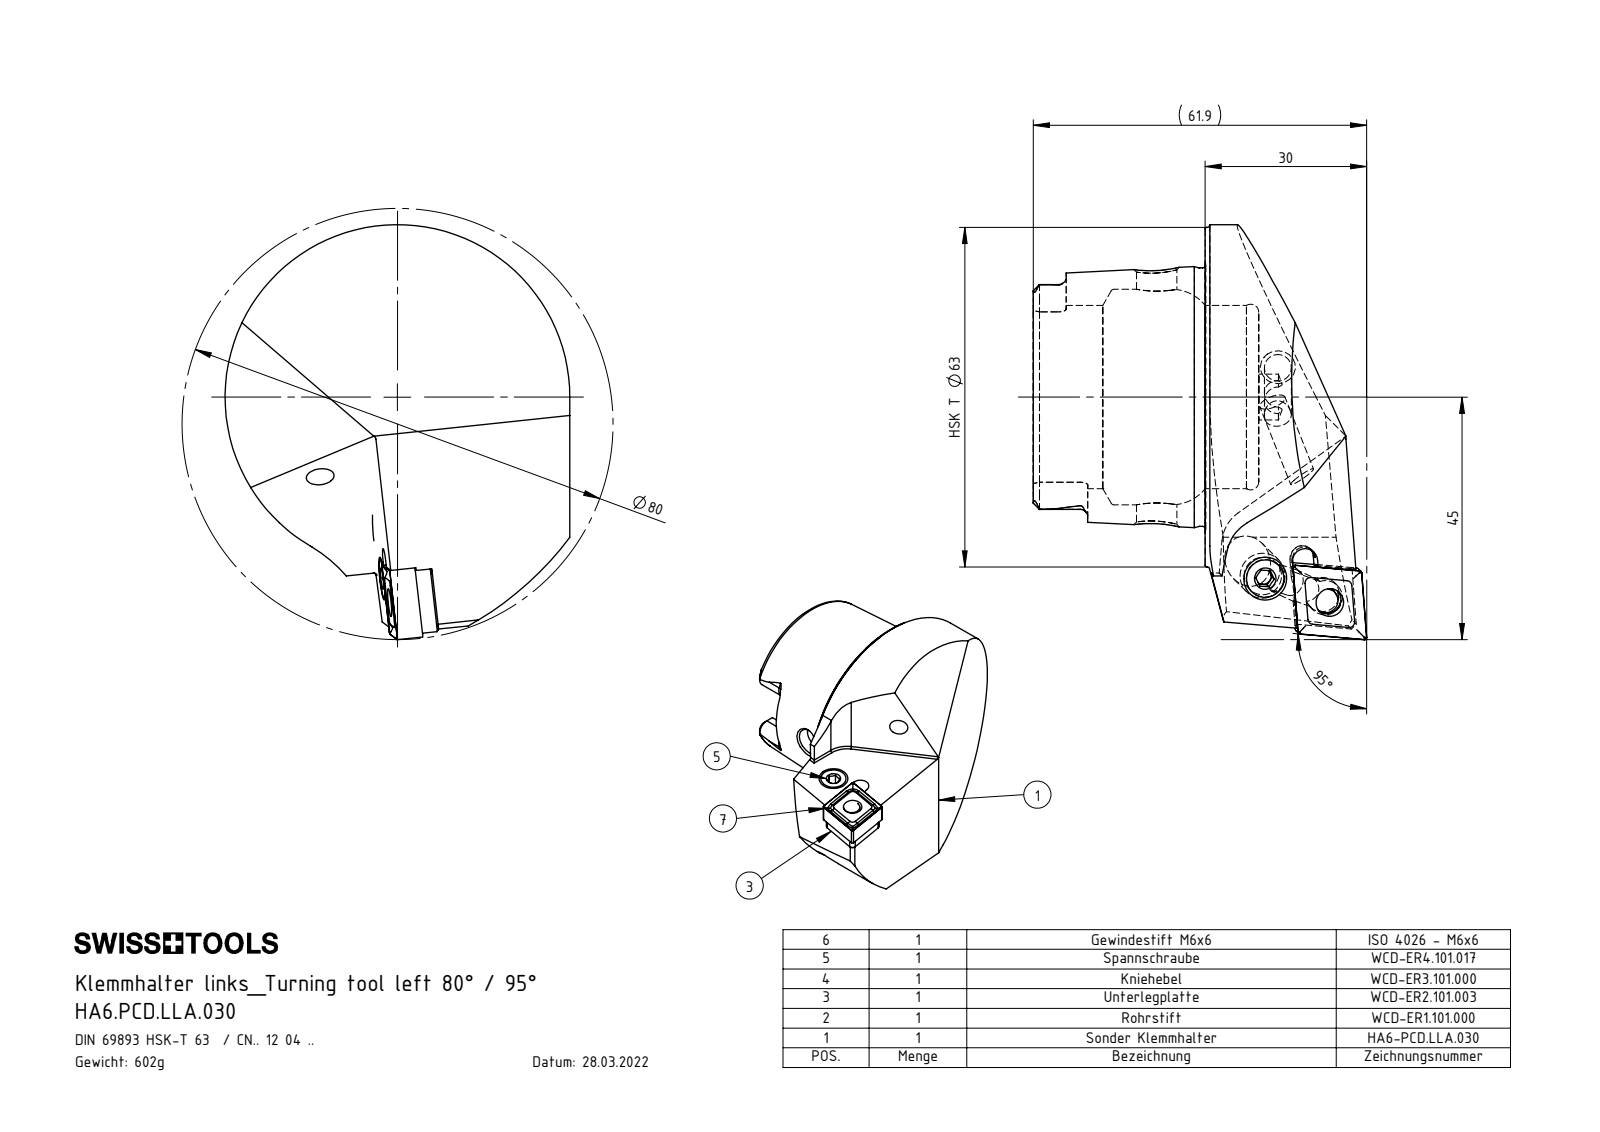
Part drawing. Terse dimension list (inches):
name: WCD-ER3.101.000_A; HA6-PCD.LLA.030_A; ISO 4026 - M6 x 6; WCD-ER4.101.017_A (+4 more)
written by: SolidWorks 2017 (AUTOMOTIVE_DESIGN)
unit: in
bodies: 7 solids, 308 faces (107 planar, 85 cylindrical, 116 other)
size: 3.031 × 2.52 × 2.437
volume: 4.64 in³; area: 38.38 in²
holes: 2× ⌀0.197, 1× ⌀0.203, 1× ⌀0.252, 1× ⌀0.276, 1× ⌀0.295, 1× ⌀0.331, 1× ⌀0.335, 1× ⌀1.339, 1× ⌀1.575
bosses: 1× ⌀2.48, 1× ⌀1.887, 1× ⌀0.315, 1× ⌀0.311, 1× ⌀0.252, 1× ⌀0.236, 1× ⌀0.177, 1× ⌀0.14
rounds: 6× R0.055, 4× R0.016, 4× R0.039, 3× R0.02, 2× R0.098, 2× R0.111, 2× R0.113, 1× R0.083
face distances: 0.392, 1.256, 1.648, 0.176, 0.125, 0.301, 0.04, 0.461, 0.46, 0.22
hole spacings: 0.504, 0.506
